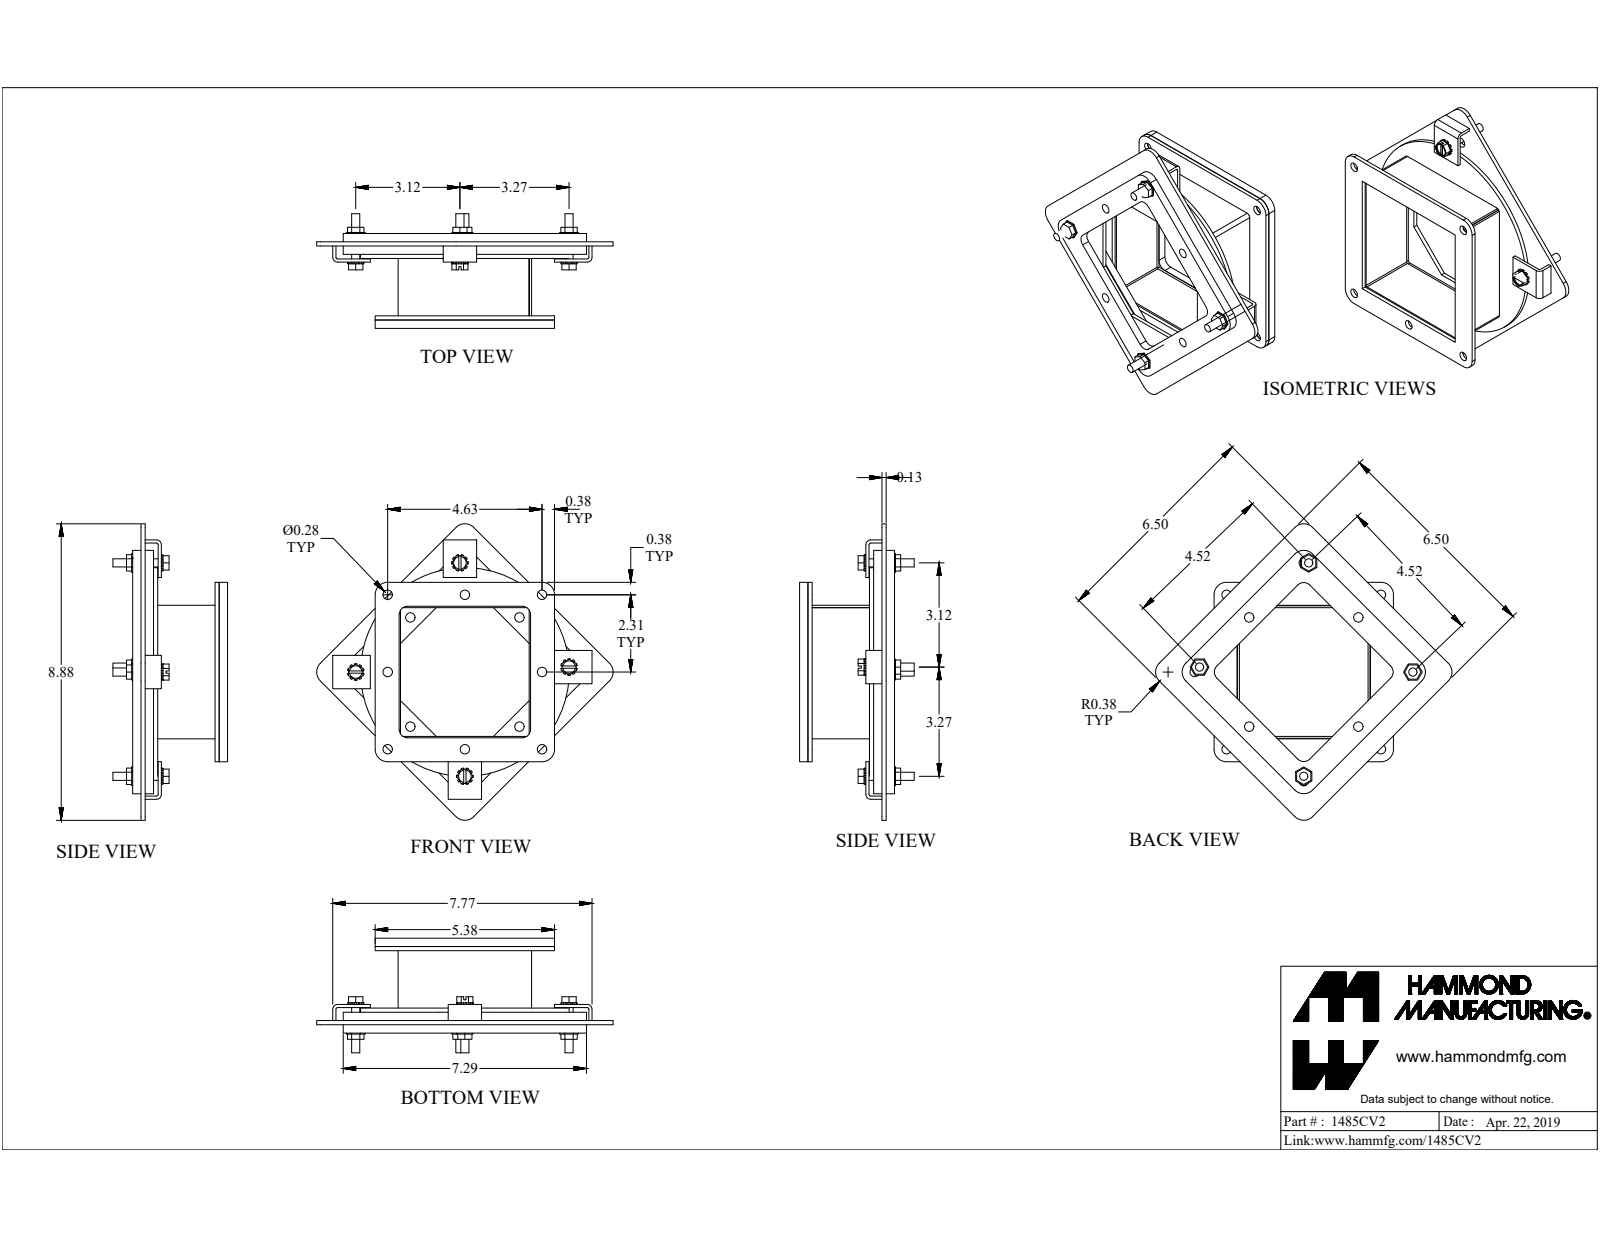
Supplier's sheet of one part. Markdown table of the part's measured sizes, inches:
| quantity | value |
| --- | --- |
| part name | 1485CV2 |
| STEP written by | SolidWorks 2019 (CONFIG_CONTROL_DESIGN) |
| units | inches |
| bodies | 33 solids, 644 faces (453 planar, 178 cylindrical, 13 other) |
| overall size | 8.882 × 8.882 × 3.434 |
| volume | 21.08 in³ |
| surface area | 350 in² |
| round holes (diameter × count) | 0.281 × 16, 0.375 × 6, 0.196 × 5, 0.258 × 4, 0.312 × 4, 0.187 × 2, 0.265 × 2, 0.313 × 2, 0.224 × 1 |
| round bosses / shafts (diameter × count) | 0.244 × 5, 0.563 × 2, 0.25 × 2, 6.25 × 1 |
| partial cylindrical surfaces (radius × count) | 0.25 × 12, 0.375 × 12, 0.048 × 9, 0.143 × 9, 0.062 × 4, 0.036 × 3, 0.108 × 3, 0.06 × 1 |
| main face-to-face distances | 0.25, 0.125, 0.375, 2.218, 0.125, 1.843, 0.375, 2.093, 2.593, 0.072 |
| hole center spacings | 2.313, 4.625, 5.171, 5.171, 4.006, 0.958, 2.503, 3.27 |
